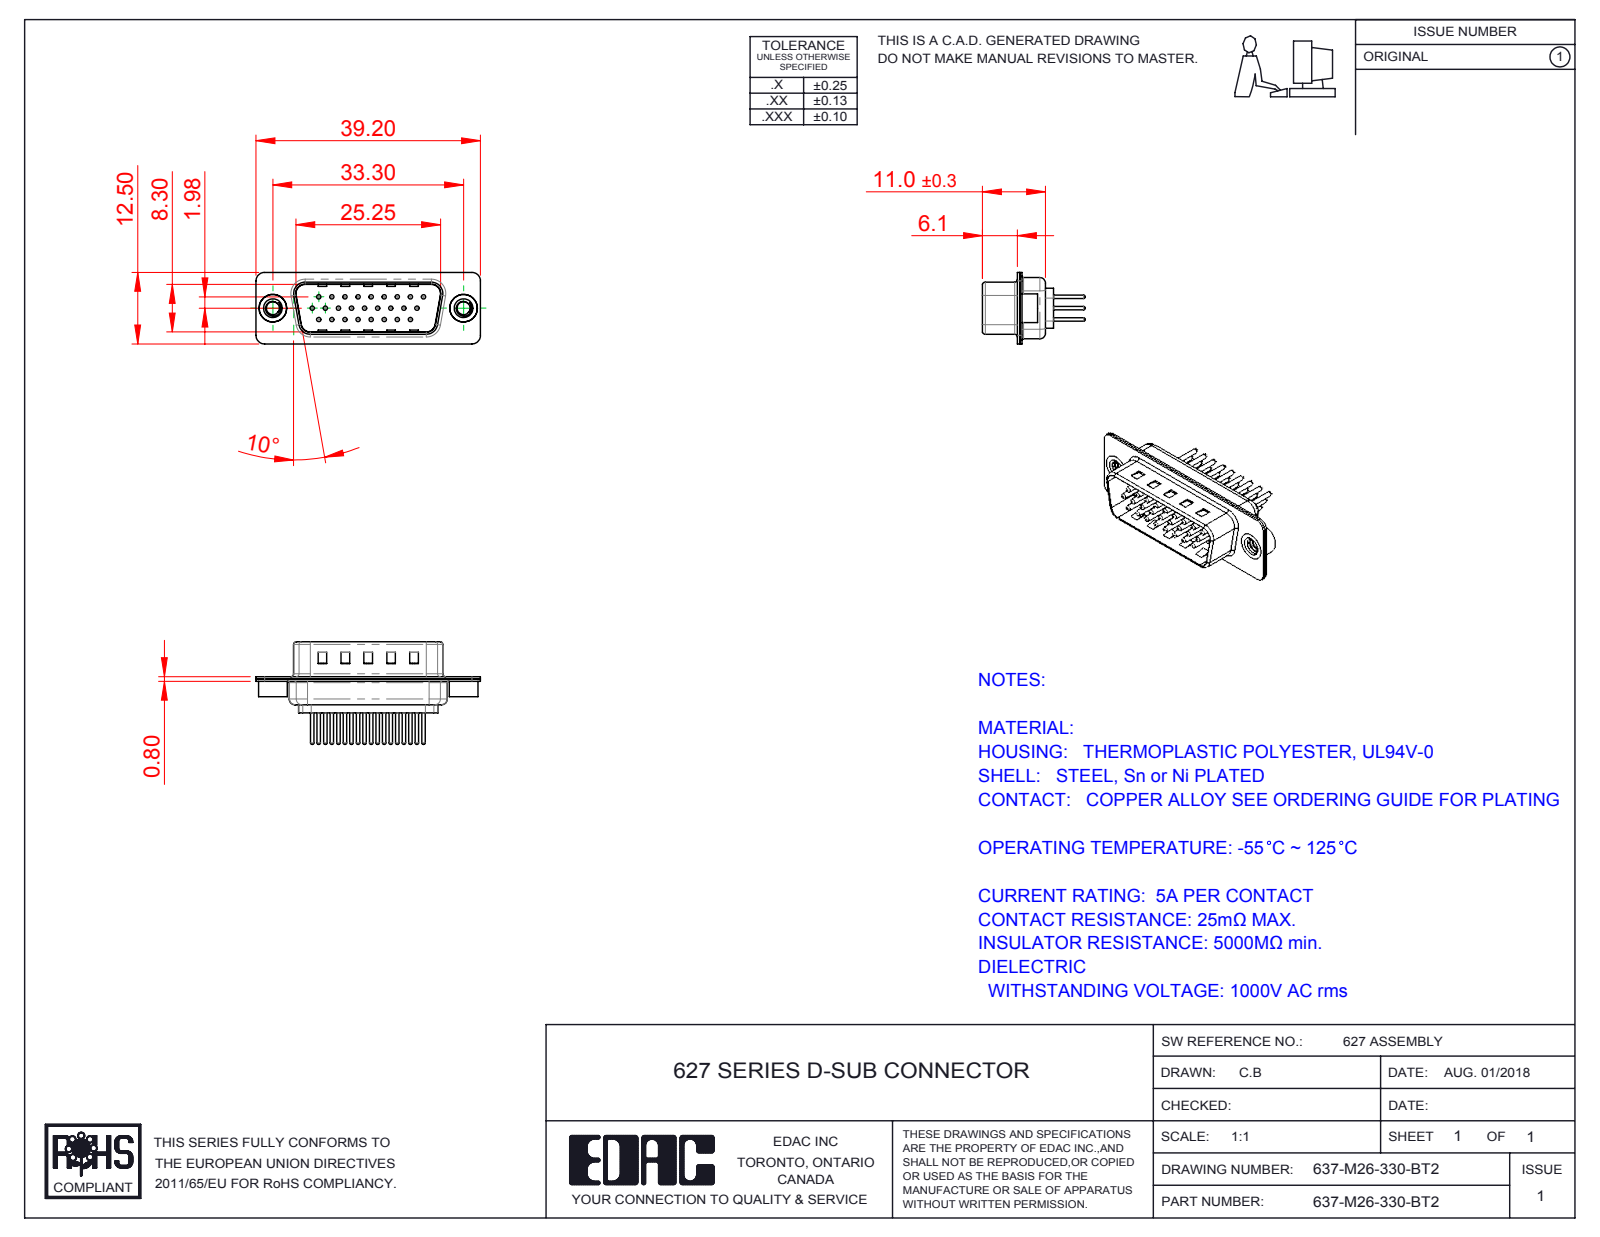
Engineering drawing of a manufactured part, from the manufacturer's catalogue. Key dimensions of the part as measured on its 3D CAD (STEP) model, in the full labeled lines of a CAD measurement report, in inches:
Part name (STEP PRODUCT): 637M Shell Rear_26 Contacts; 637M Contact Row 2_30; 637M Contact Row 1_30; 637-M26-330-BT2 (+4 more)
STEP written by: SolidWorks 2016 (CONFIG_CONTROL_DESIGN)
Units: inches
Bodies: 31 solids, 1302 faces (321 planar, 497 cylindrical, 484 other)
Overall size (bounding box): 1.543 × 0.705 × 0.492
Volume: 0.116 in³ · Surface area: 8.914 in²
Round holes (diameter × count): ⌀0.03 ×26, ⌀0.063 ×26, ⌀0.079 ×26, ⌀0.089 ×2, ⌀0.157 ×2, ⌀0.189 ×2
Round bosses / shafts (diameter × count): ⌀0.059 ×26, ⌀0.024 ×26, ⌀0.197 ×2, ⌀0.193 ×2
Partial cylindrical surfaces — rounded edges, fillets, slot ends (radius × count): R0.059 ×16, R0.079 ×12, R0.02 ×8, R0.063 ×8, R0.01 ×4, R0.024 ×4, R0.026 ×4, R0.035 ×4
Main face-to-face distances: 0.016, 0.031, 0.374, 0.358, 0.343, 0.39, 0.03, 0.217, 0.014, 0.232
Hole centre spacings: 0.156, 0.09, 0.18, 0.238, 0.09, 0.324, 0.27, 0.413
